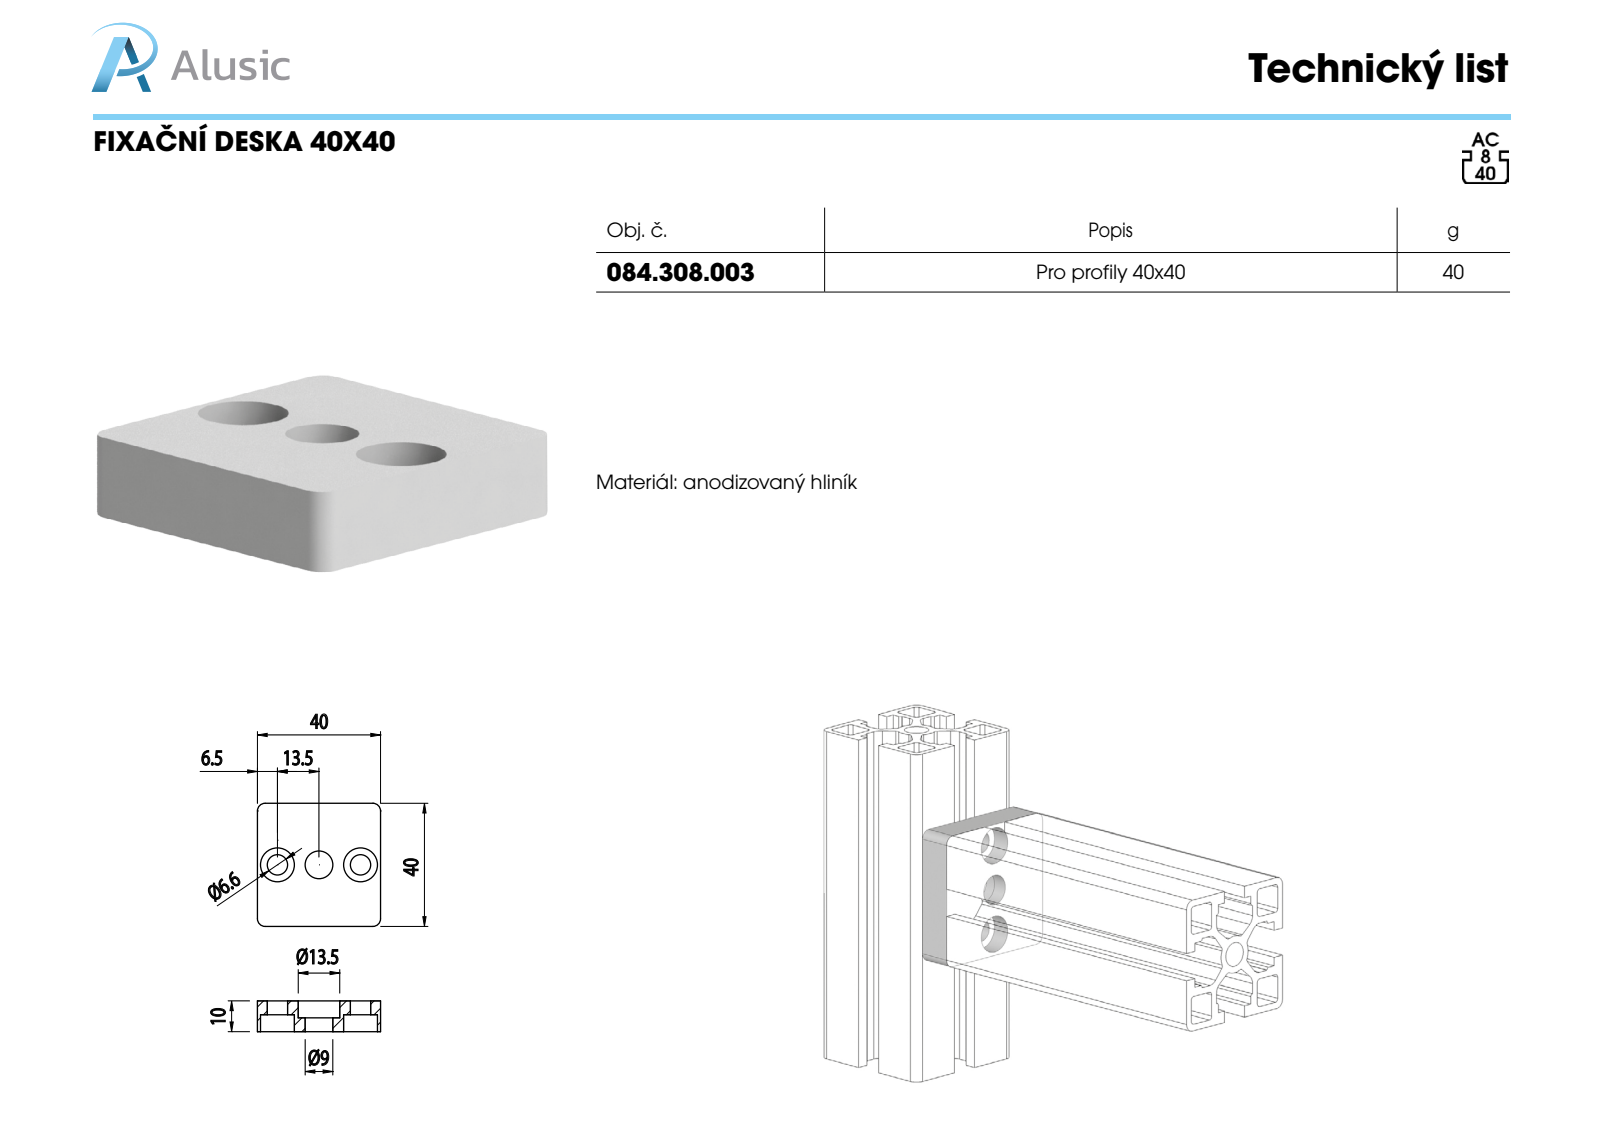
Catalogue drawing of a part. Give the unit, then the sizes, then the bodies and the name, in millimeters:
Units: millimetres
Overall size (bounding box): 40 × 40 × 10
Round holes (diameter × count): ⌀6.6 ×2, ⌀11 ×2, ⌀9 ×1, ⌀13.5 ×1
Partial cylindrical surfaces — rounded edges, fillets, slot ends (radius × count): R2.5 ×4
Main face-to-face distances: 10, 40, 4.5, 5.5, 1
Hole centre spacings: 13.5, 27
Volume: 13 520 mm³ · Surface area: 5 410 mm²
Bodies: 1 solid, 25 faces (9 planar, 16 cylindrical, 0 other)
Part name (STEP PRODUCT): 084.308.003
STEP written by: SolidWorks 2011 (CONFIG_CONTROL_DESIGN)
